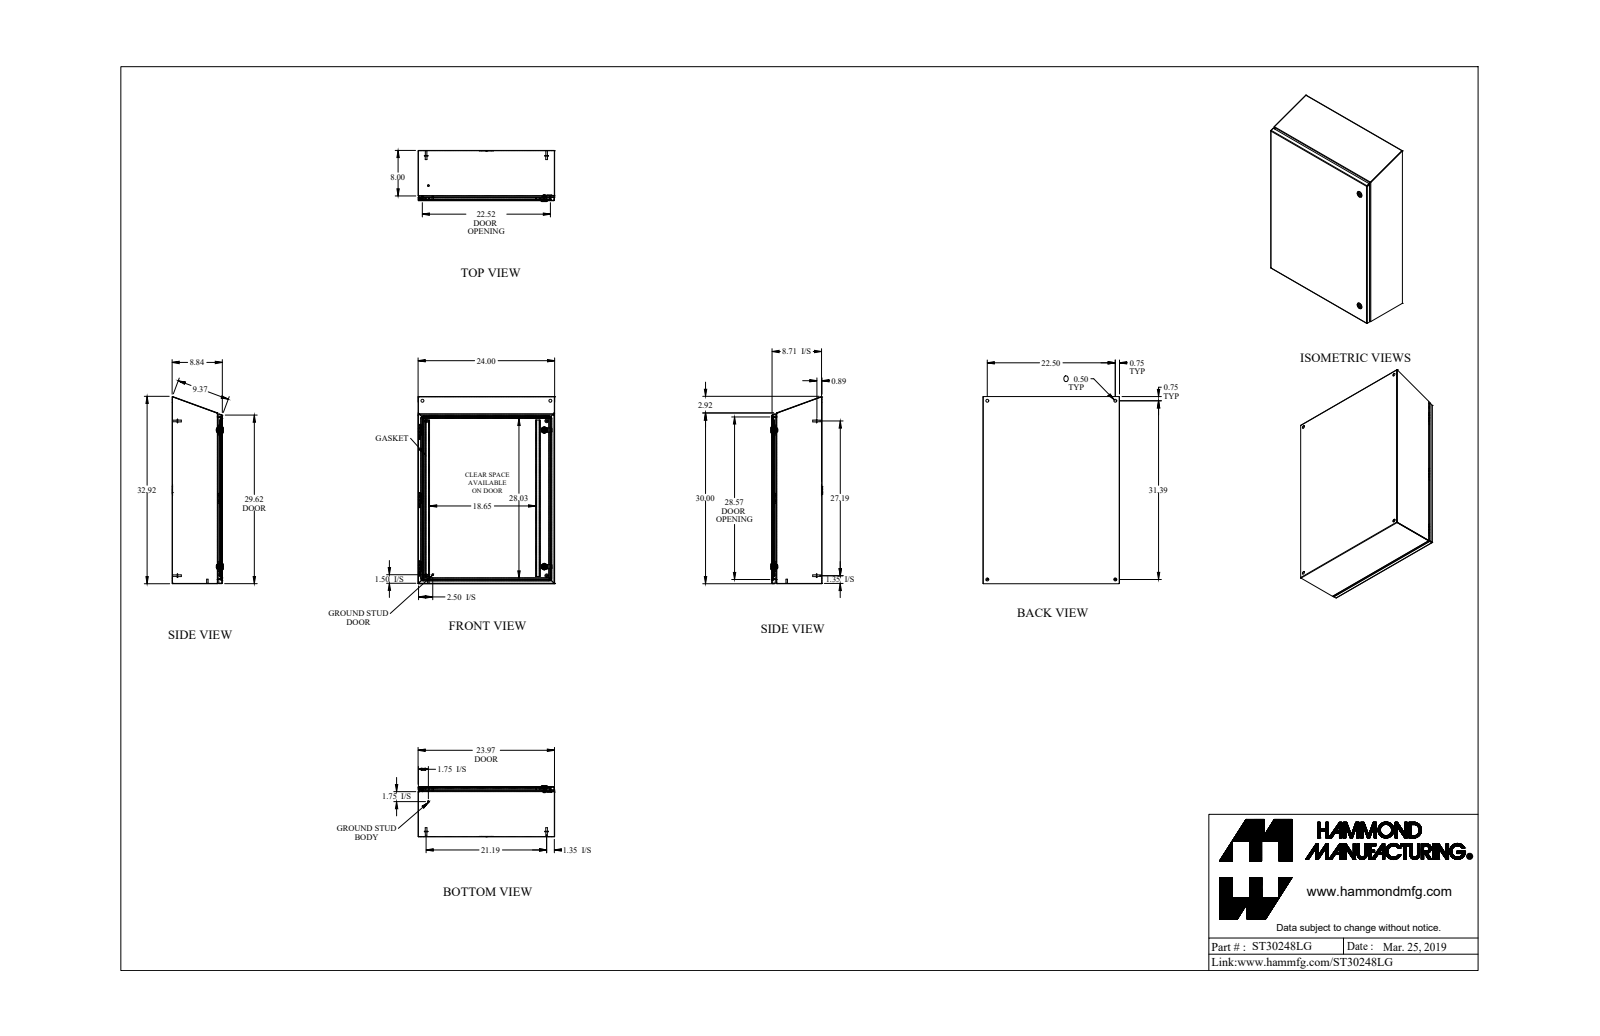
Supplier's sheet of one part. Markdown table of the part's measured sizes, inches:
| quantity | value |
| --- | --- |
| part name | ST30248LG |
| STEP written by | SolidWorks 2018 (AUTOMOTIVE_DESIGN) |
| units | inches |
| bodies | 33 solids, 868 faces (430 planar, 286 cylindrical, 152 other) |
| overall size | 32.886 × 24 × 8.997 |
| volume | 175.4 in³ |
| surface area | 5 687 in² |
| round holes (diameter × count) | 0.5 × 4, 0.232 × 2, 0.625 × 2, 0.785 × 2, 0.172 × 1, 0.24 × 1, 0.242 × 1 |
| round bosses / shafts (diameter × count) | 0.625 × 4, 0.313 × 4, 0.27 × 4, 1.1 × 2, 0.525 × 2, 0.281 × 2, 0.25 × 2, 0.455 × 1 |
| partial cylindrical surfaces (radius × count) | 0.029 × 15, 0.086 × 15, 0.188 × 13, 0.043 × 12, 0.081 × 12, 0.006 × 6, 0.062 × 6, 0.036 × 4 |
| main face-to-face distances | 0.057, 8.708, 8.765, 0.072, 8.837, 8.78, 23.943, 23.886, 24, 7.943 |
| hole center spacings | 22.5, 31.386, 38.618, 2.494, 5.246, 21.544, 22.033, 24 |
